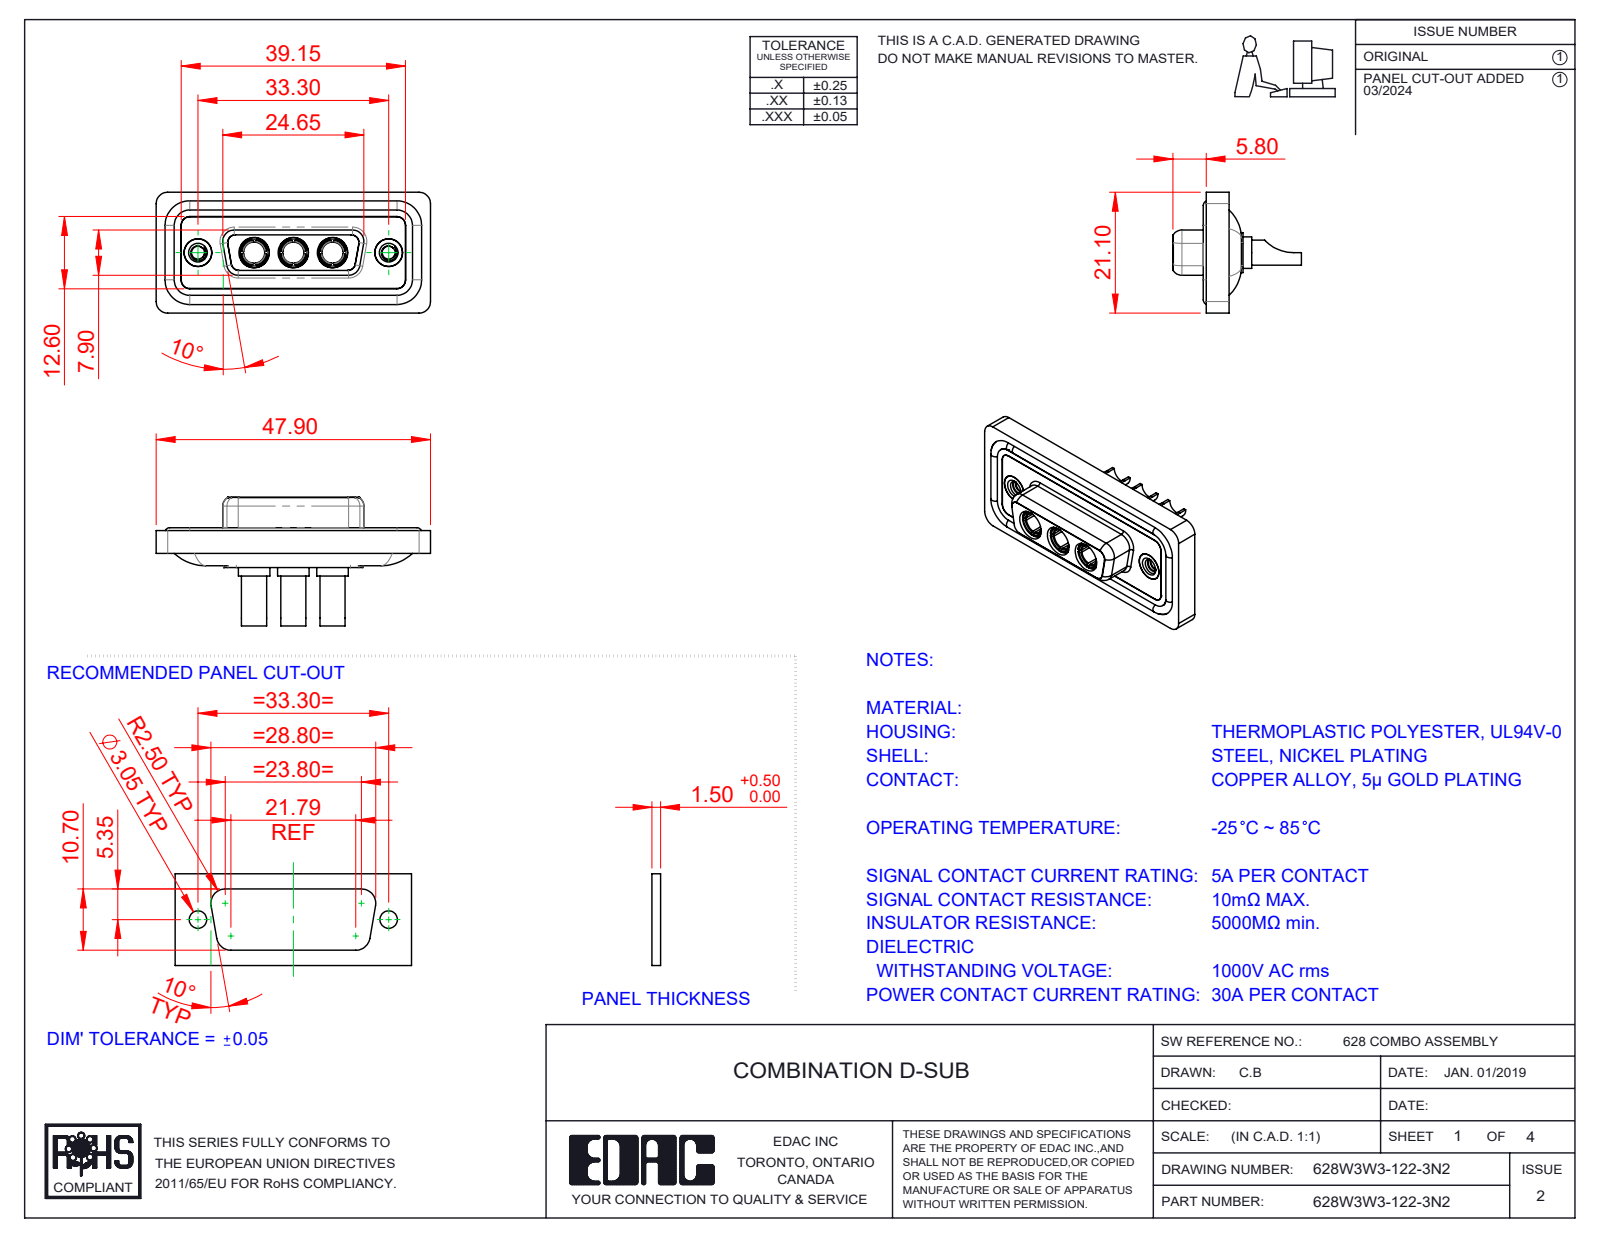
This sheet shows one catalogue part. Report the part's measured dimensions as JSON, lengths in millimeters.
{"part_name": "628Combo Shell Rear_15 Contacts; 628Combo Waterproof Housing_15 Contacts; 628Combo Housing_3W3; Power Socket_30A SC (+3 more)", "step_written_by": "SolidWorks 2023 (CONFIG_CONTROL_DESIGN)", "units": "millimeters", "bodies": {"solids": 13, "faces": 626, "planar": 201, "cylindrical": 266, "other": 159}, "overall_size": [47.9, 22.45, 21.1], "volume_mm3": 6098, "surface_area_mm2": 10061, "round_holes": [[4.85, 5], [3.5, 3], [3.7, 3], [5.3, 3], [2.26, 2], [4, 2], [4.05, 2], [5, 2]], "round_bosses_or_shafts": [[1.6, 4], [5.5, 3], [5.2, 3], [4.96, 3], [4.75, 3], [4.4, 3], [3.75, 3], [4.95, 2]], "partial_cylinders_radius": [[1.5, 22], [2, 20], [1.35, 12], [1.6, 8], [0.25, 4], [0.5, 4], [0.6, 4], [0.65, 4]], "face_to_face_distances": [0.4, 1.8, 1.6, 0.5, 7.45, 1.1, 2.9, 5.65, 7.05, 6.6], "hole_center_spacings": [6.85, 9.8, 16.65, 23.5, 13.7, 33.3]}
